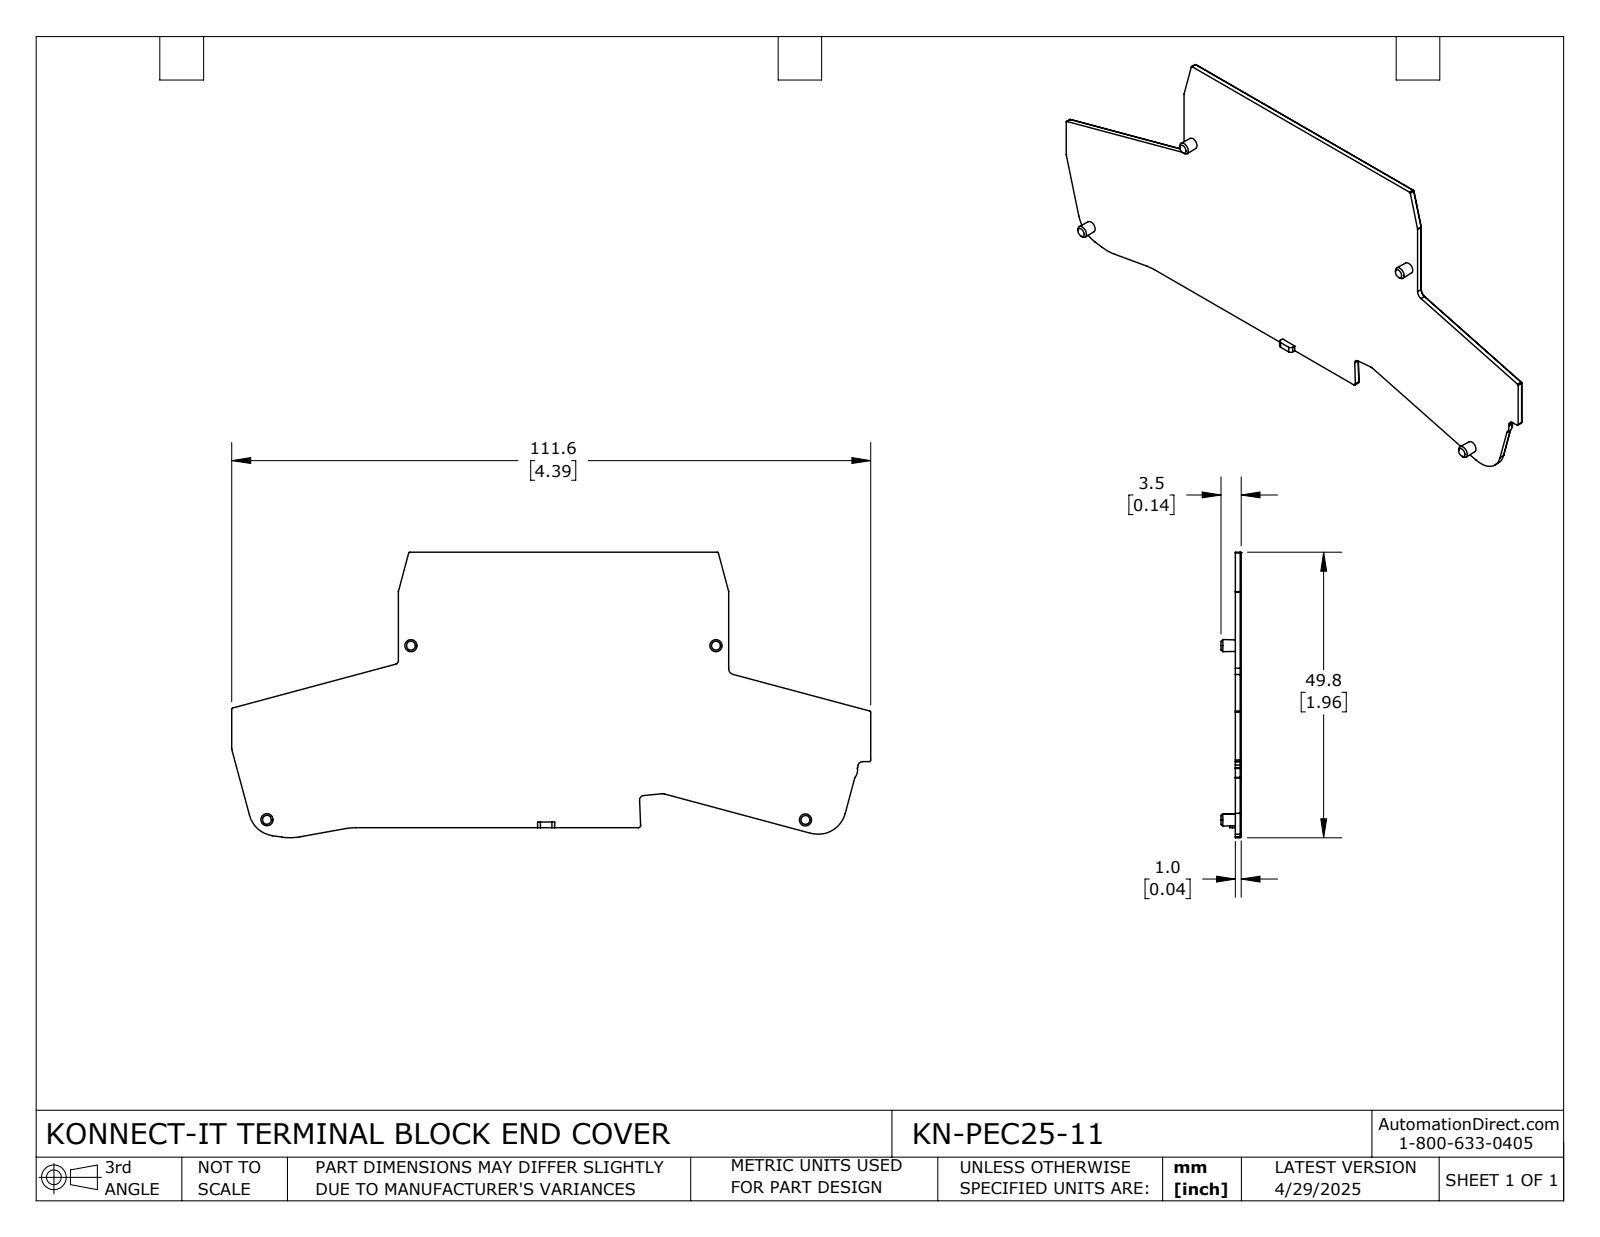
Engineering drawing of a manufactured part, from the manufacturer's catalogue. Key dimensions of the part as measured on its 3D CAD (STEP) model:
Part name (STEP PRODUCT): KN-PEC25-11
STEP written by: SolidWorks 2024 (CONFIG_CONTROL_DESIGN)
Units: inches
Bodies: 1 solid, 117 faces (51 planar, 50 cylindrical, 16 other)
Overall size (bounding box): 4.393 × 1.962 × 0.138
Volume: 0.242 in³ · Surface area: 12.77 in²
Partial cylindrical surfaces — rounded edges, fillets, slot ends (radius × count): R0.008 ×8, R0.004 ×7, R0.012 ×4, R0.016 ×3, R0.02 ×2, R0.043 ×2, R0.047 ×2, R0.189 ×2
Main face-to-face distances: 0.039, 1.893, 0.033, 0.916, 1.889, 2.271, 0.977, 0.912, 0.098, 0.132
